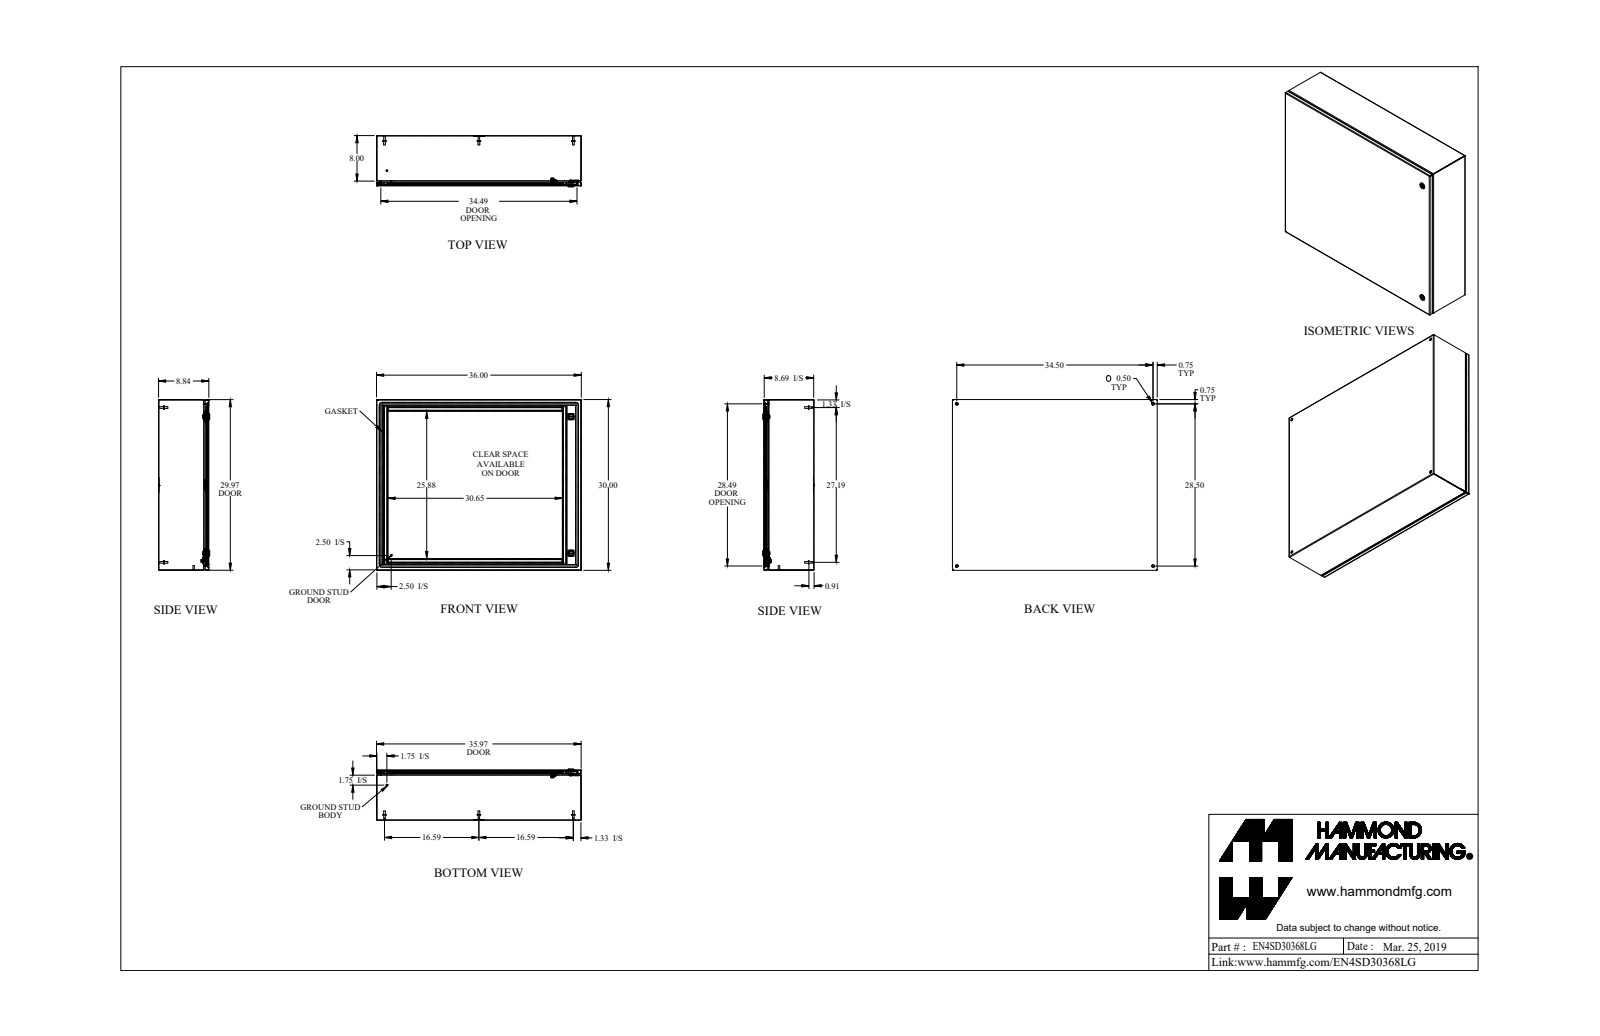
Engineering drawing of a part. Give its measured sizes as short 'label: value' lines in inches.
name: EN4SD30368LG_Default
written by: SolidWorks 2019 (CONFIG_CONTROL_DESIGN)
unit: in
bodies: 39 solids, 1153 faces (547 planar, 383 cylindrical, 223 other)
size: 36 × 30 × 8.997
volume: 272 in³; area: 7 698 in²
holes: 4× ⌀0.5, 2× ⌀0.232, 2× ⌀0.625, 2× ⌀0.785, 1× ⌀0.172, 1× ⌀0.196, 1× ⌀0.24, 1× ⌀0.242, 1× ⌀0.275, 1× ⌀0.375
bosses: 7× ⌀0.625, 6× ⌀0.313, 6× ⌀0.27, 2× ⌀1.1, 2× ⌀0.525, 2× ⌀0.281, 2× ⌀0.25, 1× ⌀0.455
rounds: 24× R0.043, 24× R0.081, 20× R0.036, 20× R0.108, 14× R0.062, 10× R0.094, 10× R0.312, 9× R0.016
face distances: 0.072, 8.765, 8.693, 8.837, 29.928, 35.928, 29.856, 30, 35.856, 36
hole spacings: 28.5, 33.503, 34.5, 44.749, 2.493, 2.494, 3.542, 4.441
